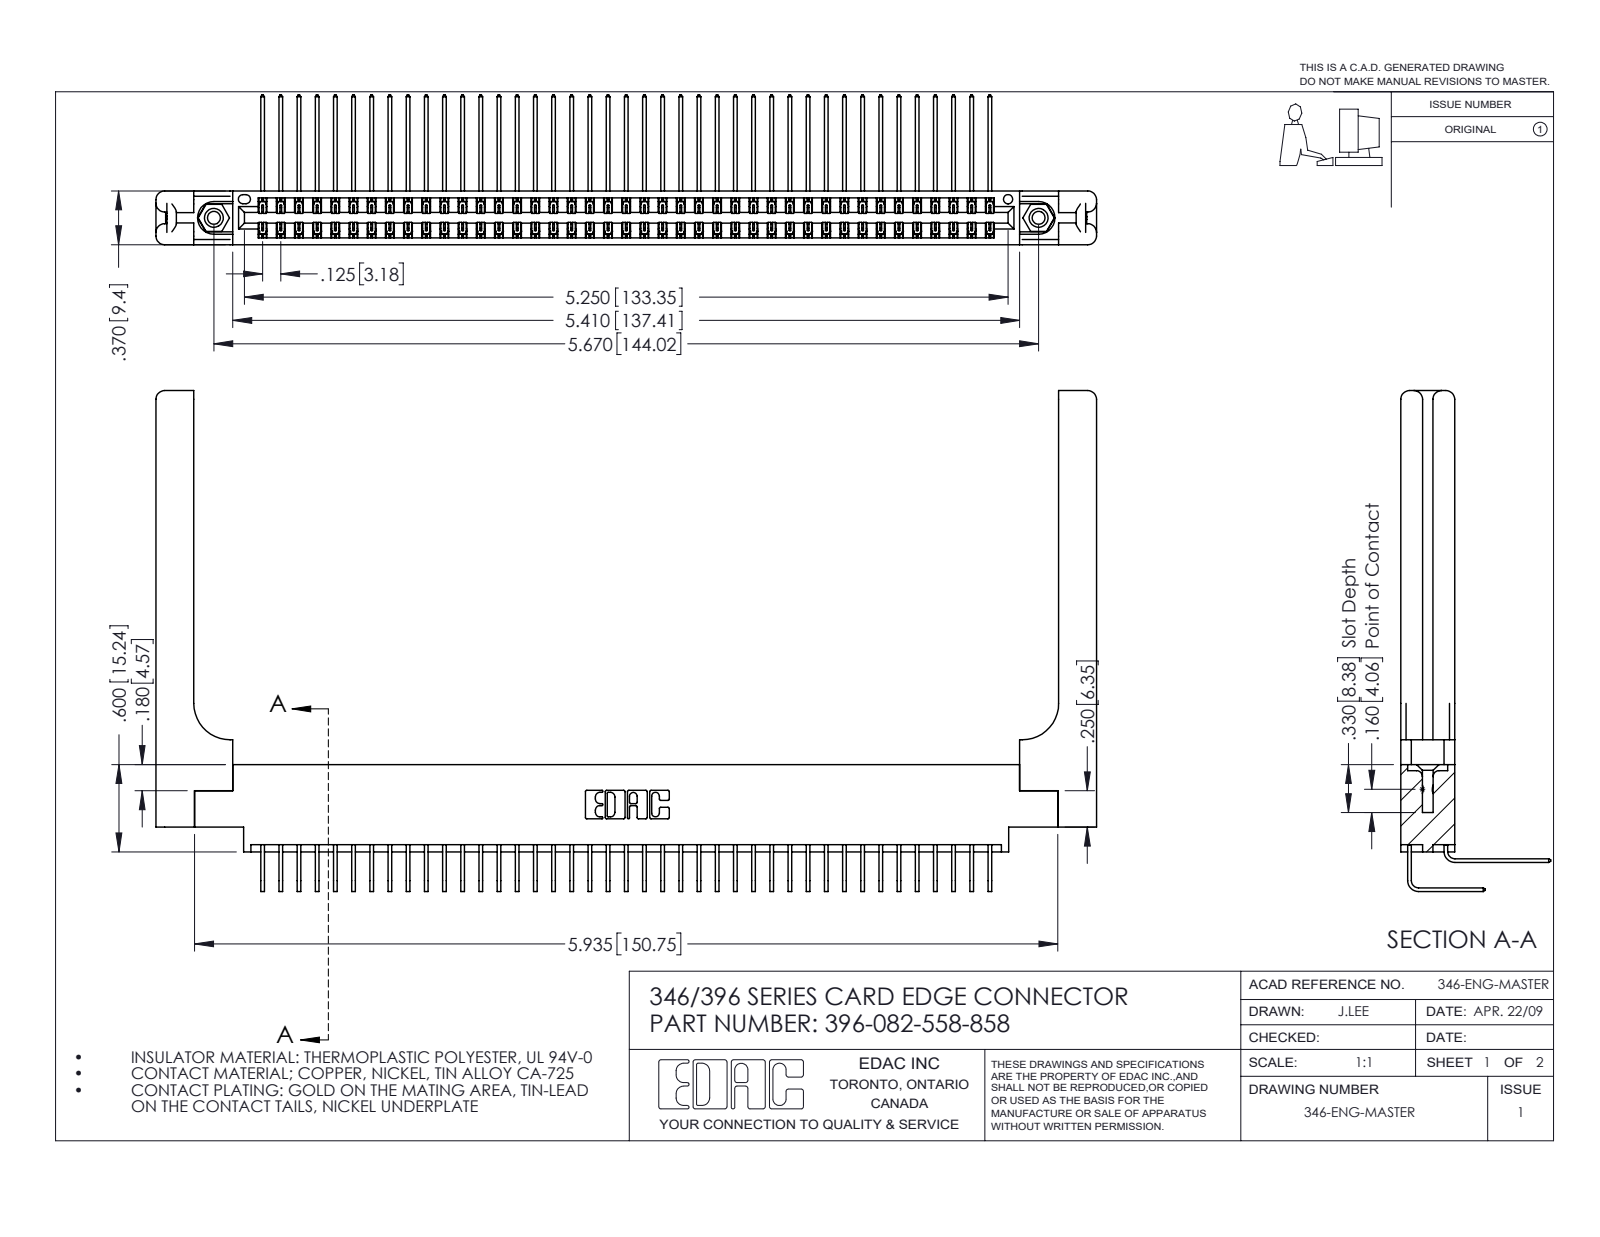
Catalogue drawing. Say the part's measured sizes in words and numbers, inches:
The part is named "345-250-001_345-250-001-102; 346 Part_0.170 Offset - 0.156 Dia-TH; 345-292-001_558 559 Tail - 1; 396-082-558-858 (+2 more)". Its 3-D file was written by "SolidWorks 2016 (CONFIG_CONTROL_DESIGN)". It is 87 solids with 4810 faces: 3262 planar, 1488 cylindrical and 60 other. Overall it measures 6.466 by 3.443 by 1.03 inches. Its volume is 1.454 cubic inches and its surface area 46.26 square inches. Round holes: 2 of diameter 0.089, 2 of diameter 0.125, 2 of diameter 0.156, 1 of diameter 0.064. Round bosses or shafts: 2 of diameter 0.155. Partial cylindrical surfaces (rounded edges, fillets, slot ends): 123 of radius 0.006, 22 of radius 0.01, 16 of radius 0.06, 6 of radius 0.007, 6 of radius 0.031, 3 of radius 0.026, 2 of radius 0.014, 2 of radius 0.022. The main face-to-face distances are 0.322, 0.37, 0.048, 0.072, 0.025, 0.298, 0.148, 0.15, 0.25, 0.275. The hole center spacings are 0.246, 5.461, 5.67.
